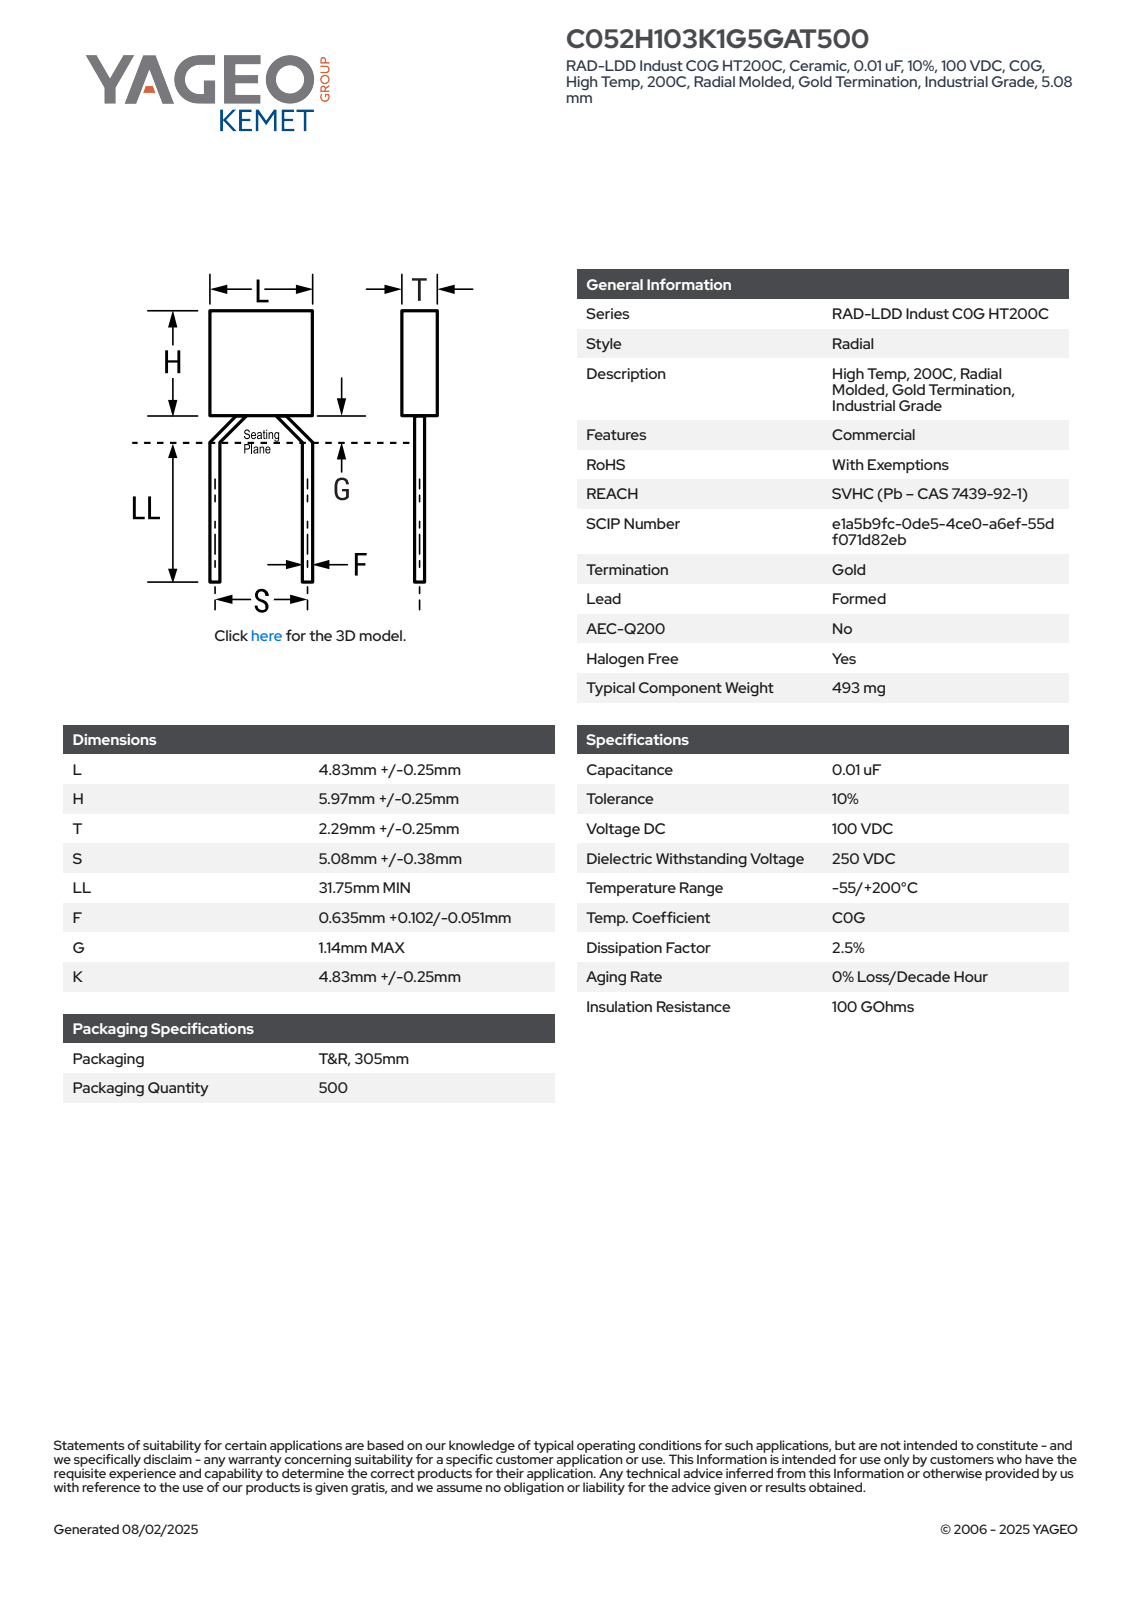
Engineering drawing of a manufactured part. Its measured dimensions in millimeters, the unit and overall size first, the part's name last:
Units: millimetres
Overall size (bounding box): 39.11 × 5.82 × 2.54
Round bosses / shafts (diameter × count): ⌀0.74 ×2
Main face-to-face distances: 2.54, 5.08, 6.22, 32.89, 39.11, 0.81, 36.31, 3.42, 2.8, 35.5
Volume: 108 mm³ · Surface area: 277 mm²
Bodies: 4 solids, 73 faces (65 planar, 4 cylindrical, 4 other)
Part name (STEP PRODUCT): CCR_RMHS_C052_L5.08H6.22T2.54S5.08LL31.75F0.737G1.14
STEP written by: SolidWorks 2014 (AUTOMOTIVE_DESIGN)
